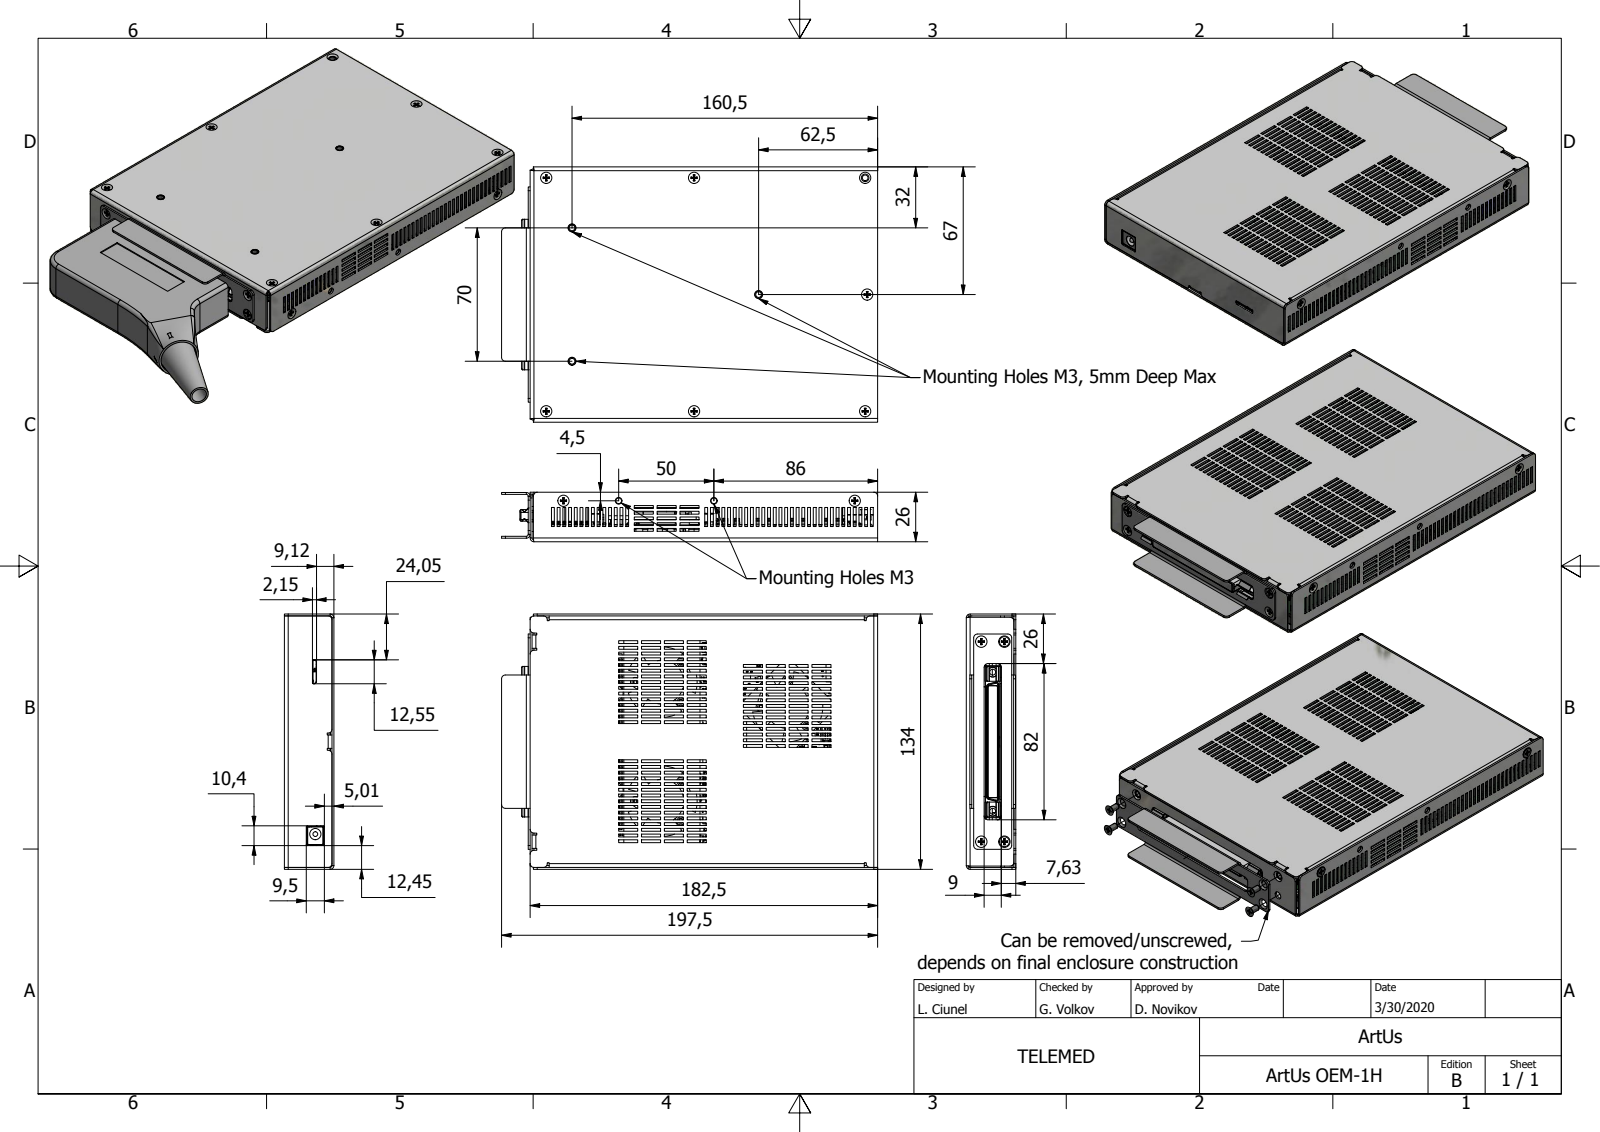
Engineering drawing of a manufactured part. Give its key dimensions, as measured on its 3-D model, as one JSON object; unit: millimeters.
{"part_name": "ArtUs OEM VerB; EKR OEM BOT Ver B; EKR OEM Bot Ver B; ArtUs-1H_REV-D (+7 more)", "step_written_by": "Autodesk Inventor 2020 (AUTOMOTIVE_DESIGN)", "units": "millimeters", "bodies": {"solids": 1855, "faces": 79256, "planar": 42784, "cylindrical": 10593, "other": 25879}, "overall_size": [197.5, 134.4, 26.2], "volume_mm3": 177316, "surface_area_mm2": 328082, "round_holes": [[0.7, 280], [0.8, 27], [0.5, 19], [3.2, 13], [4, 11], [0.4, 6], [3, 5], [3.1, 5], [4.2, 5], [1.5, 3], [0.3, 2], [1.27, 2]], "round_bosses_or_shafts": [[0.6, 896], [1, 34], [5, 13], [0.45, 12], [10, 6], [0.89, 6], [6, 5], [5.2, 4]], "partial_cylinders_radius": [[0.3, 600], [0.15, 256], [0.4, 200], [0.2, 198], [0.1, 173], [0.13, 120], [0.5, 99], [0.12, 16]], "face_to_face_distances": [1, 2, 7.86, 8.86, 6.86, 5.86, 133, 132, 134, 0.7], "hole_center_spacings": [1.57, 1.6, 2.75, 4.22, 3.2, 4.19, 4.8, 122.5]}
